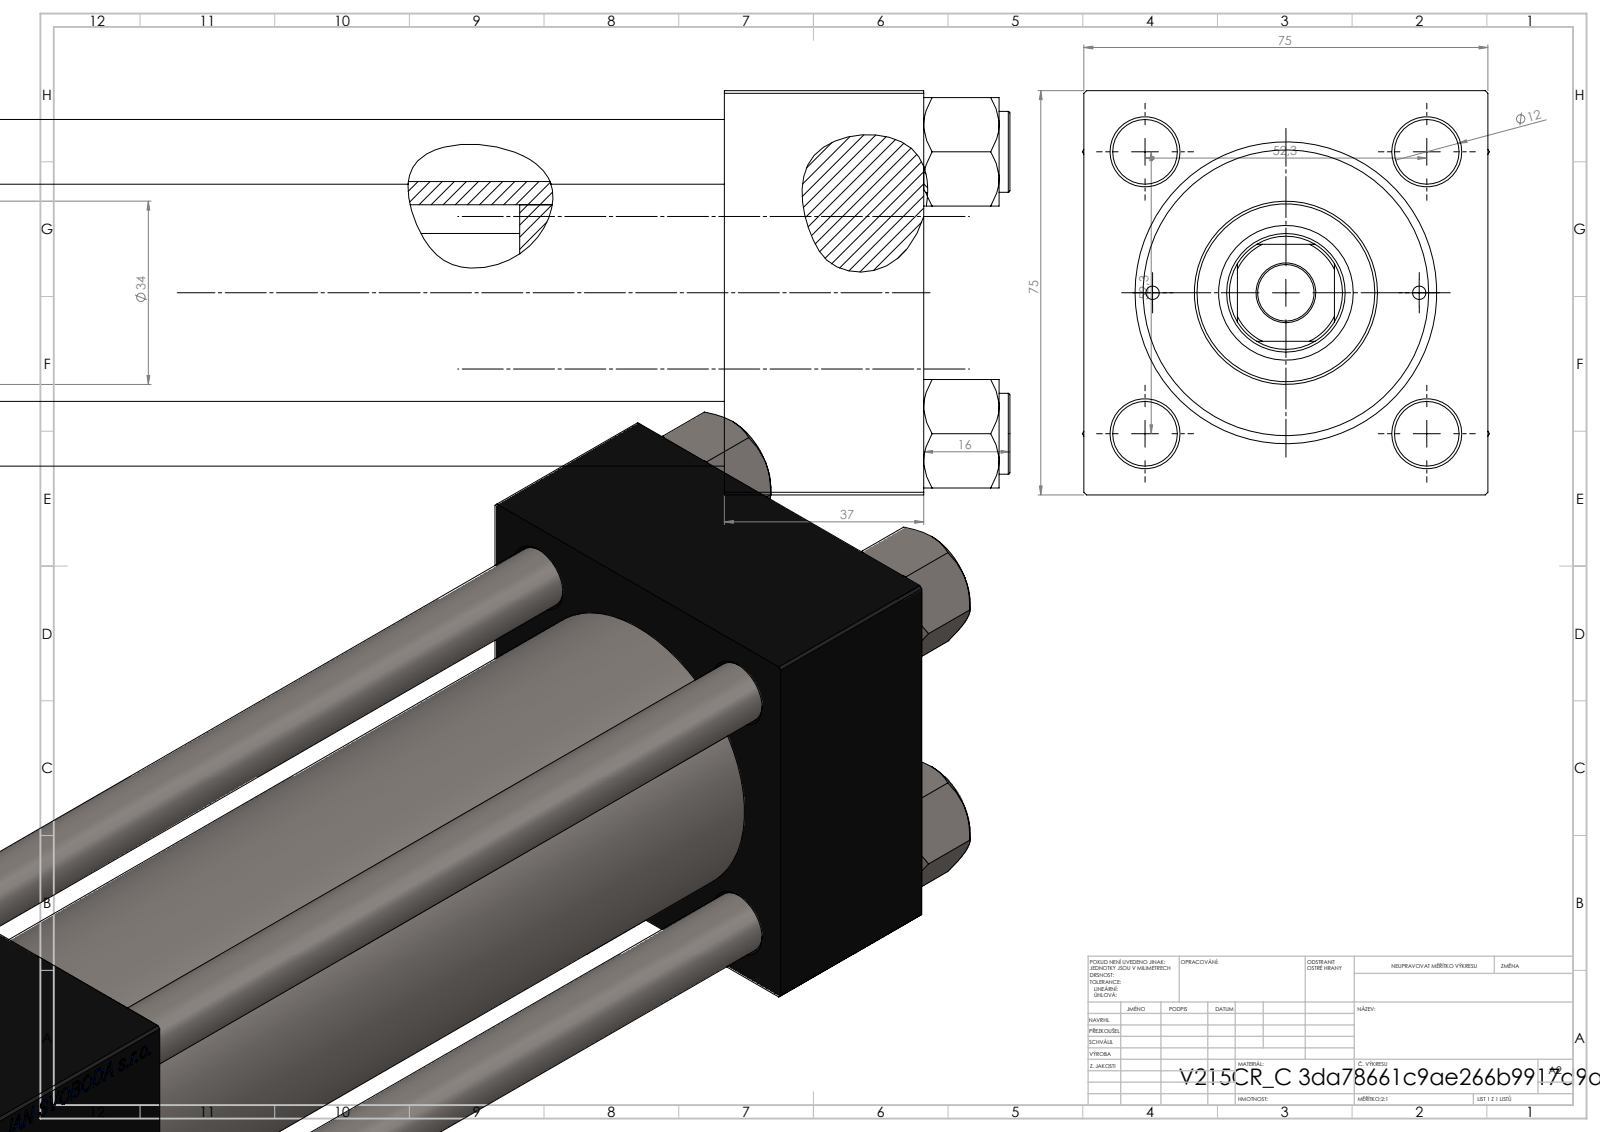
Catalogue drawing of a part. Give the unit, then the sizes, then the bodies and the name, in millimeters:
Units: millimetres
Overall size (bounding box): 300 × 75.54 × 75
Round holes (diameter × count): ⌀12 ×4, ⌀2.5 ×2, ⌀7 ×2, ⌀20.96 ×2, ⌀30 ×2, ⌀10.5 ×1, ⌀22 ×1, ⌀25 ×1, ⌀41 ×1, ⌀50 ×1, ⌀53 ×1
Round bosses / shafts (diameter × count): ⌀15 ×4, ⌀56 ×1, ⌀34 ×1
Partial cylindrical surfaces — rounded edges, fillets, slot ends (radius × count): R10.5 ×1
Main face-to-face distances: 75, 37, 259, 222, 200, 163, 59, 230.3, 193.3, 30.3
Hole centre spacings: 26.19, 36.98, 52.3, 57.22, 24.75, 73.96, 49.5, 198.5
Volume: 796 687 mm³ · Surface area: 205 421 mm²
Bodies: 11 solids, 1155 faces (528 planar, 91 cylindrical, 536 other)
Part name (STEP PRODUCT): V215_VC_A; NUT_M5_C; V215CR_C_TYCINKA; V215CR_C_Body (+1 more)
STEP written by: SolidWorks 2019 (CONFIG_CONTROL_DESIGN)
